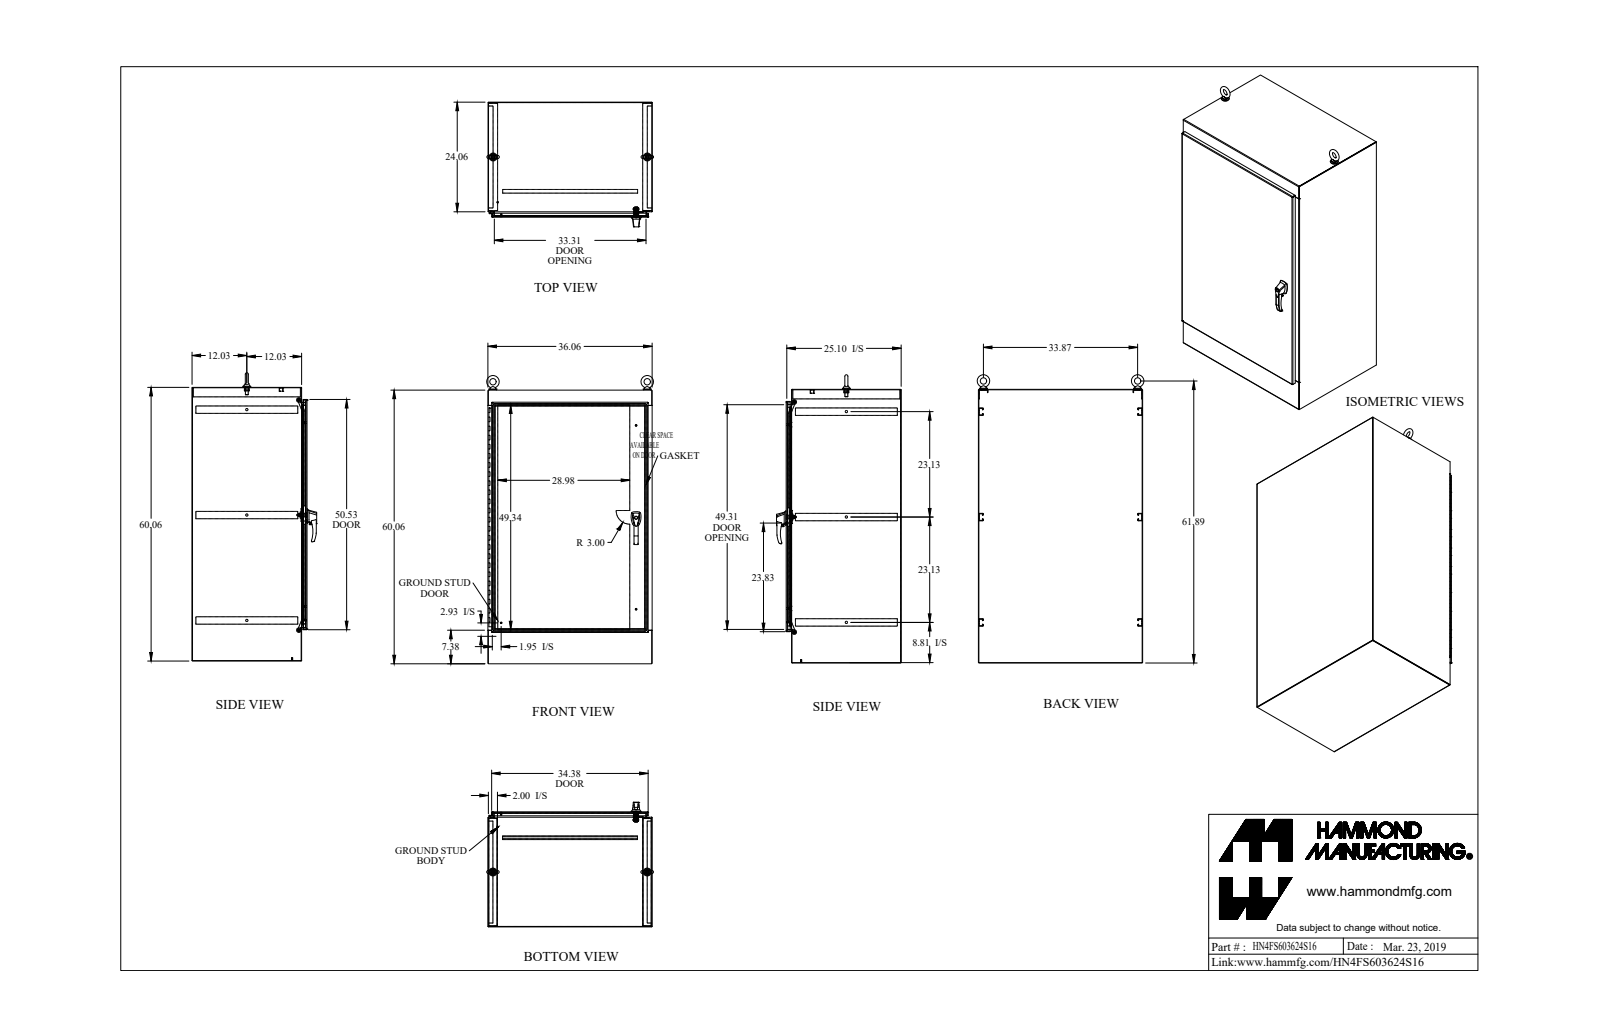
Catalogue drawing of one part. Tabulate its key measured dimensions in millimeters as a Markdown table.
| quantity | value |
| --- | --- |
| part name | HN4FS603624S16 |
| STEP written by | SolidWorks 2018 (AUTOMOTIVE_DESIGN) |
| units | millimeters |
| bodies | 56 solids, 1763 faces (820 planar, 778 cylindrical, 165 other) |
| overall size | 1606.7 × 929.7 × 695 |
| volume | 16 930 000 mm³ |
| surface area | 13 980 000 mm² |
| round holes (diameter × count) | 7.7 × 8, 8.9 × 7, 12.7 × 3, 6.4 × 2, 6.5 × 2, 7.1 × 2, 7.1 × 2, 8 × 2, 9.9 × 2, 10.5 × 2, 13.4 × 2, 17.3 × 2 |
| round bosses / shafts (diameter × count) | 44.5 × 2, 38.1 × 2, 31.8 × 2, 25.4 × 2, 19.1 × 2, 18.7 × 2, 16 × 2, 15.9 × 2 |
| partial cylindrical surfaces (radius × count) | 1.1 × 42, 3.5 × 36, 12.7 × 23, 3.2 × 22, 0.5 × 16, 1.5 × 15, 1.2 × 13, 3.6 × 13 |
| main face-to-face distances | 2.4, 638.9, 913.5, 636.4, 911.1, 641.3, 1523.1, 915.9, 608.7, 30.1 |
| hole center spacings | 152.4, 304.8, 457.2, 609.6, 762, 28.6, 32.7, 188.8 |
